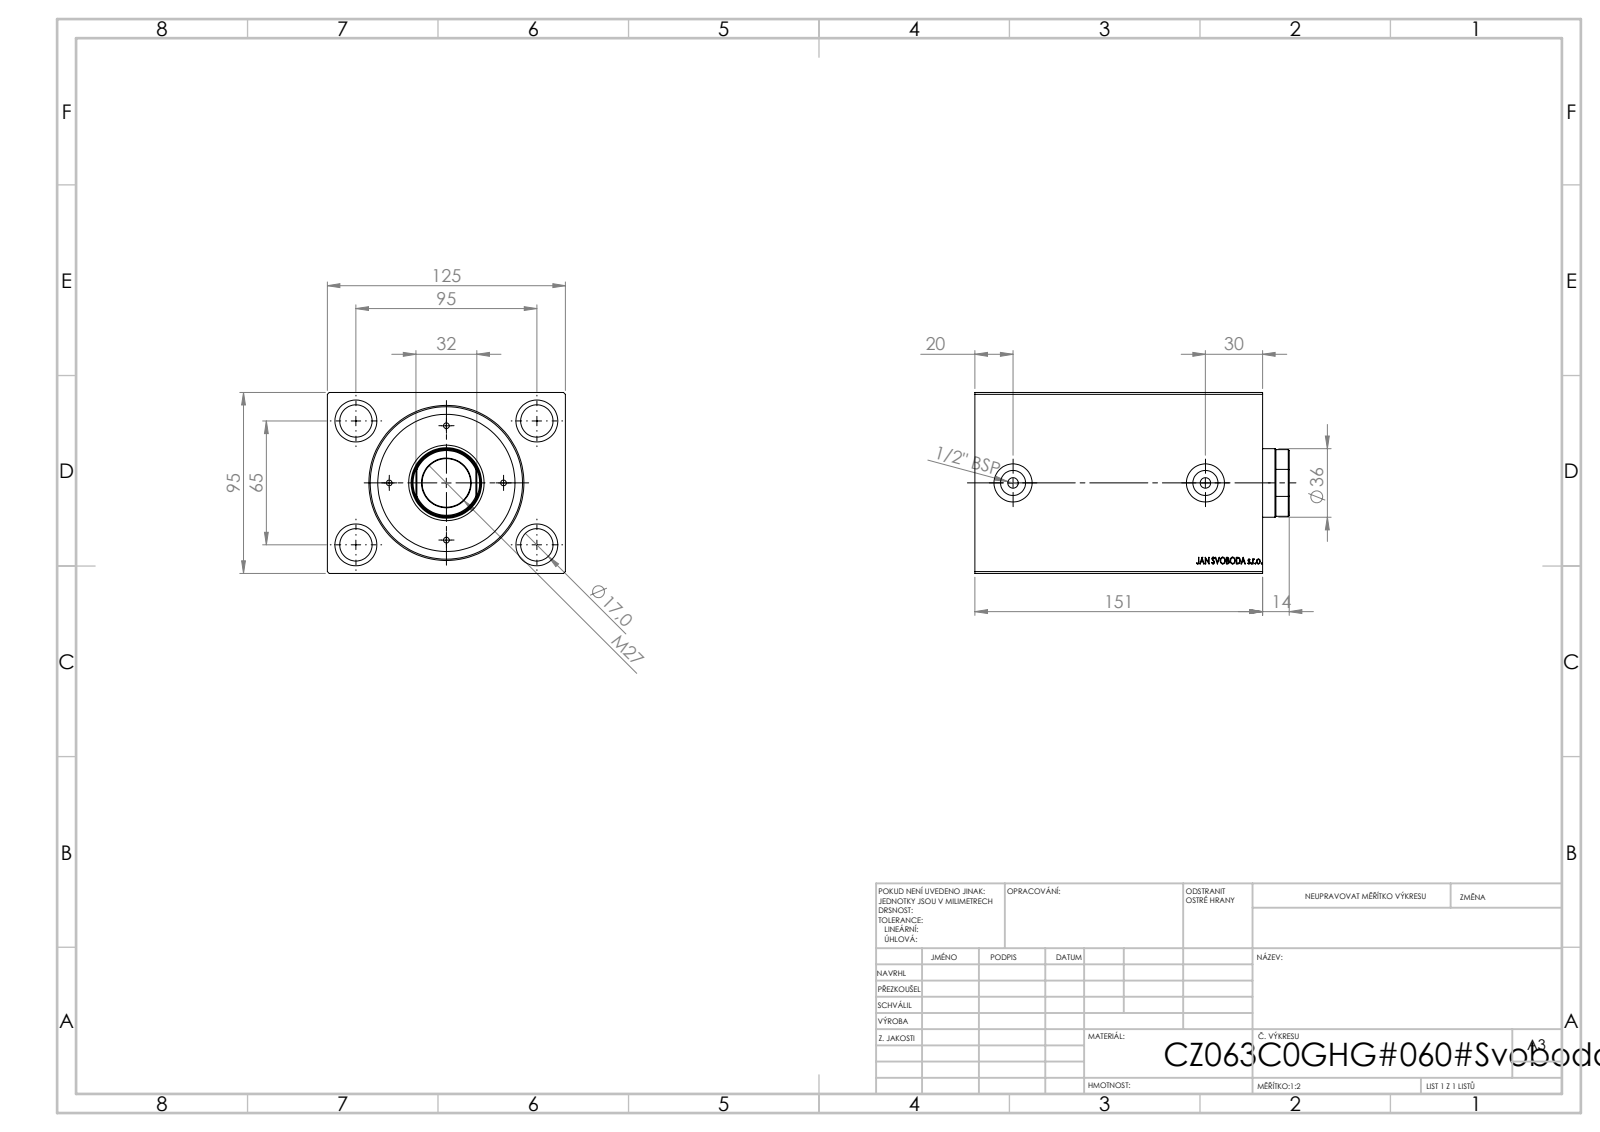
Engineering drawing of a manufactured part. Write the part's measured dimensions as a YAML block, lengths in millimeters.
step_written_by: "SolidWorks 2019 (CONFIG_CONTROL_DESIGN)"
units: millimeters
bodies: {solids: 1, faces: 825, planar: 397, cylindrical: 46, other: 382}
overall_size: [151, 125, 95]
volume: 1206000
surface_area: 149581
round_holes:
  - {diameter: 17, count: 4}
  - {diameter: 22, count: 4}
  - {diameter: 5.5, count: 2}
  - {diameter: 8, count: 2}
  - {diameter: 13.16, count: 2}
  - {diameter: 20, count: 2}
  - {diameter: 36, count: 1}
  - {diameter: 63, count: 1}
  - {diameter: 80, count: 1}
face_to_face_distances: [95, 125, 151, 130.2, 20.8, 14, 116.2, 137, 10.33, 140.67]
hole_center_spacings: [57.55, 65, 95, 115.11, 81, 101]
